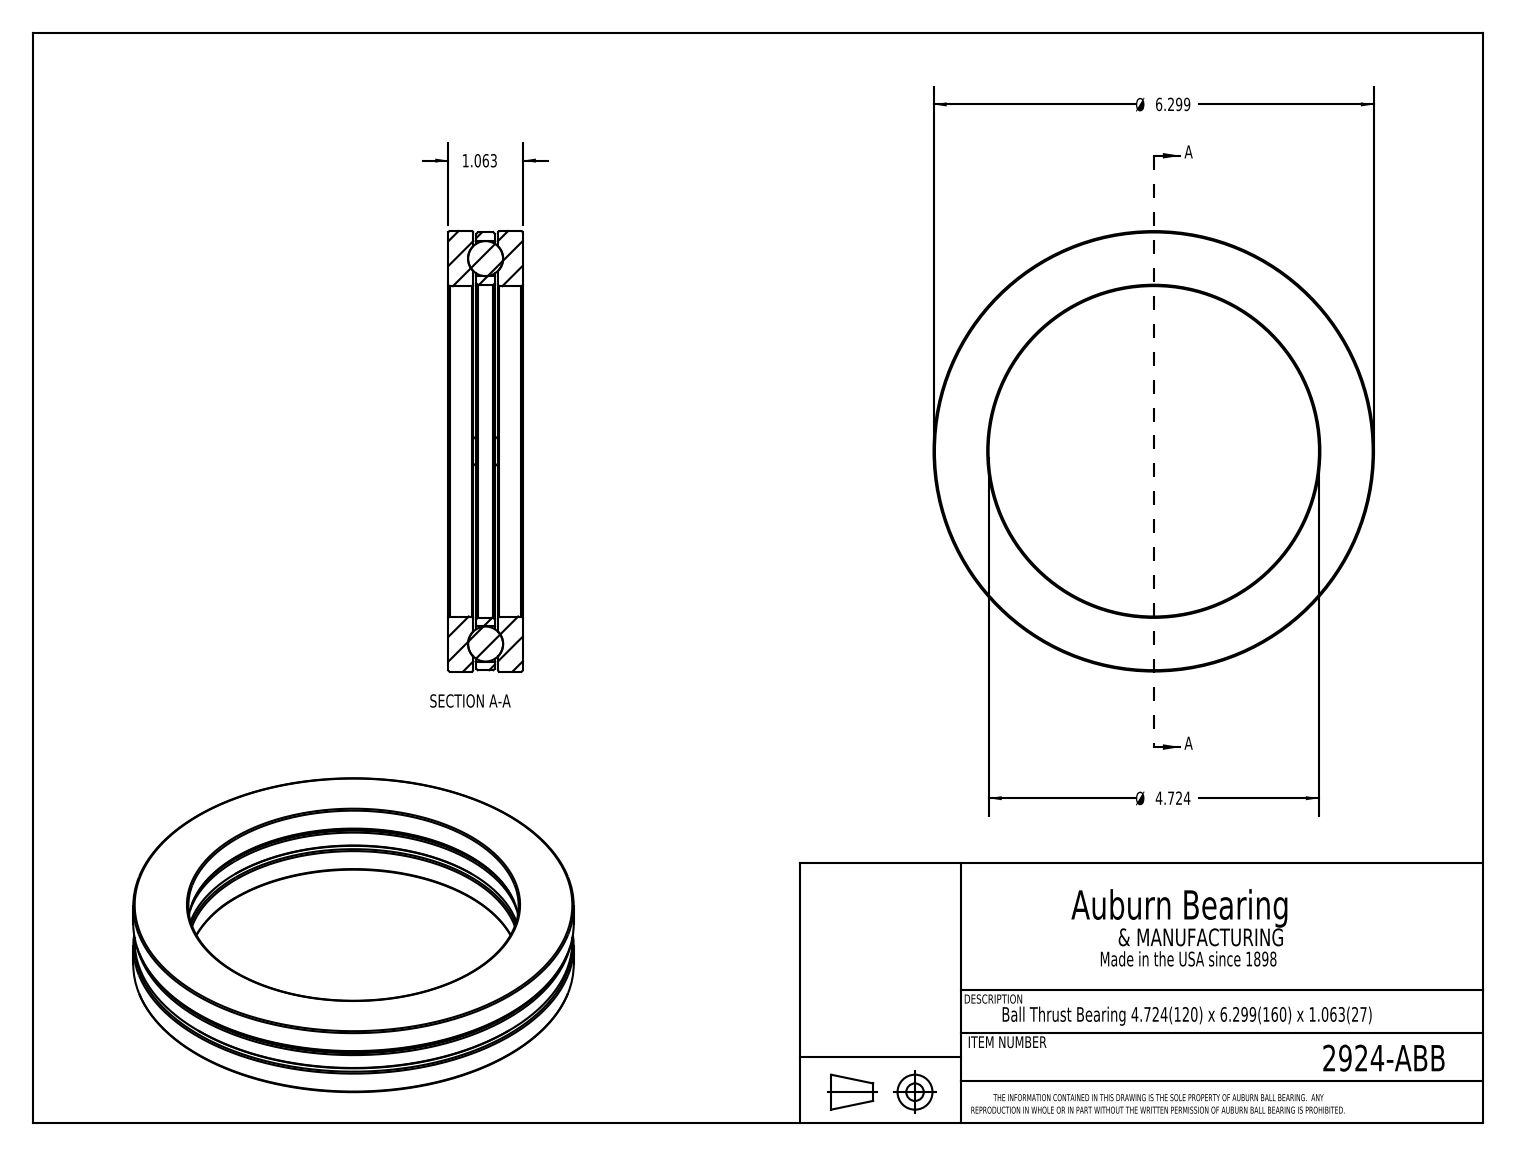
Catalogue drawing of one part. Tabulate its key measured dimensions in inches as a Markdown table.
| quantity | value |
| --- | --- |
| part name | 2924-ABB |
| STEP written by | SolidWorks 2017 (CONFIG_CONTROL_DESIGN) |
| units | inches |
| bodies | 7 solids, 36 faces (8 planar, 10 cylindrical, 18 other) |
| overall size | 6.299 × 6.299 × 1.063 |
| volume | 12.51 in³ |
| surface area | 116.7 in² |
| round holes (diameter × count) | 0.51 × 4, 4.724 × 1, 4.764 × 1 |
| round bosses / shafts (diameter × count) | 6.299 × 1, 6.259 × 1 |
| main face-to-face distances | 0.398, 0.665, 0.354, 0.709, 0.044, 0.31, 1.063, 0.266 |
| hole center spacings | 2.756, 3.897, 5.512 |
